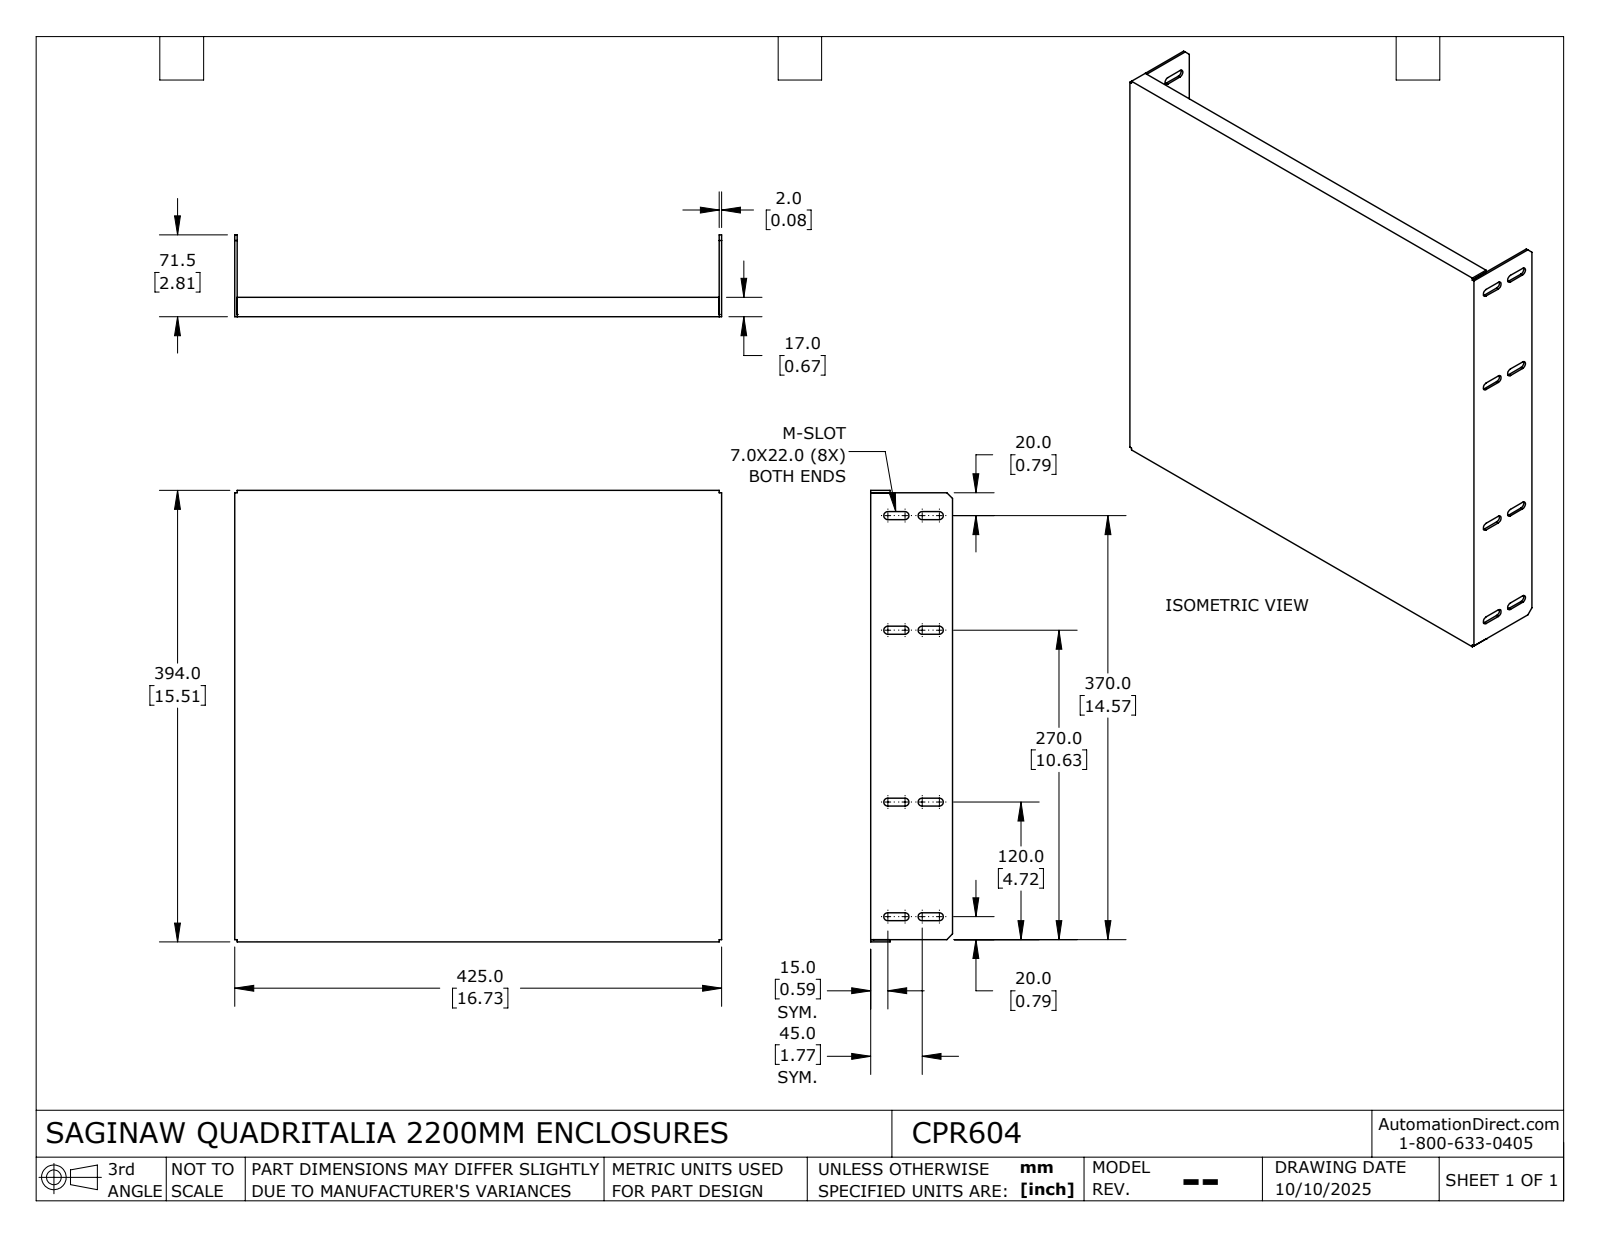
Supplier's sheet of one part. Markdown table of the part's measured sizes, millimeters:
| quantity | value |
| --- | --- |
| part name | CPR604_Default |
| STEP written by | SolidWorks 2024 (CONFIG_CONTROL_DESIGN) |
| units | millimeters |
| bodies | 1 solid, 91 faces (59 planar, 32 cylindrical, 0 other) |
| overall size | 425 × 394 × 71.5 |
| volume | 463 855 mm³ |
| surface area | 469 447 mm² |
| partial cylindrical surfaces (radius × count) | 3.5 × 16 |
| main face-to-face distances | 2, 423, 425, 421, 392, 394, 390, 17, 15, 71.5 |
